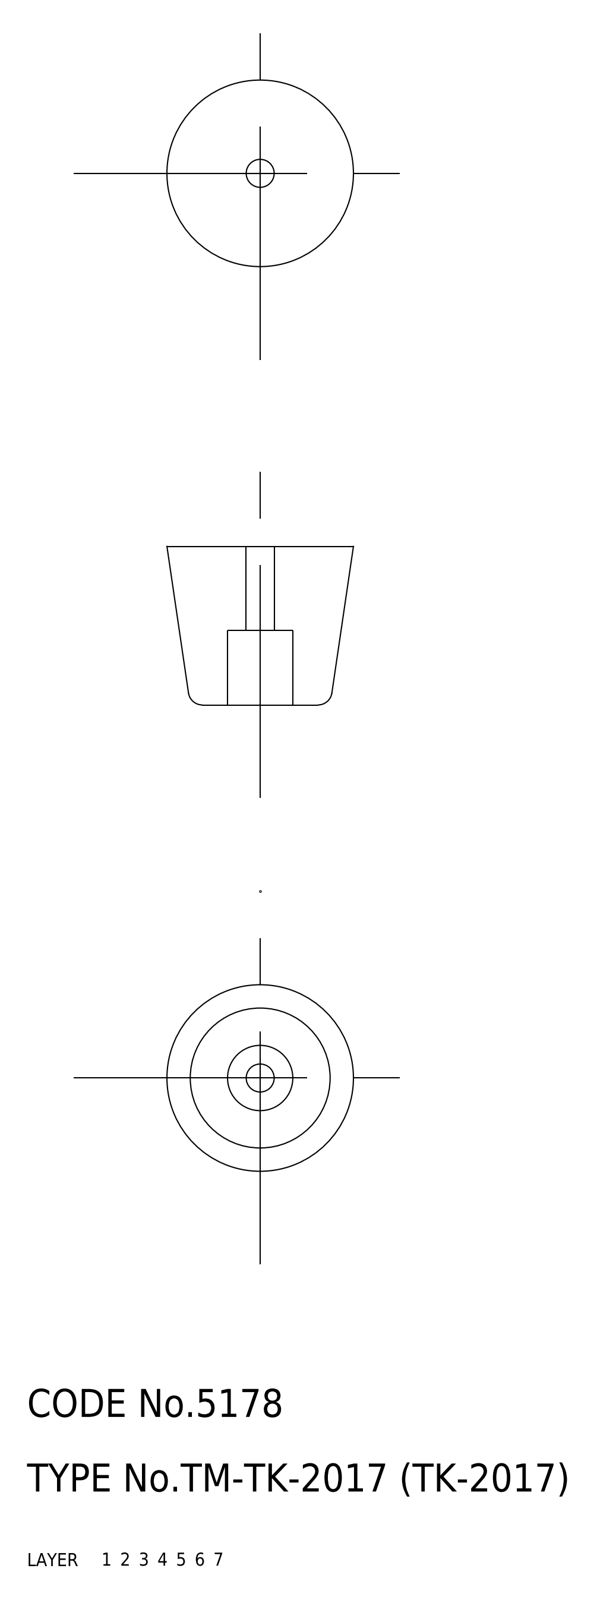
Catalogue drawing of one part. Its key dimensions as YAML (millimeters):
part_name: "washer; rubber foot; TK_2017_9330_36"
step_written_by: "CADfix (AUTOMOTIVE_DESIGN)"
units: millimeters
bodies: {solids: 2, faces: 23, planar: 0, cylindrical: 0, other: 23}
overall_size: [20, 20, 17]
volume: 3739
surface_area: 1859
